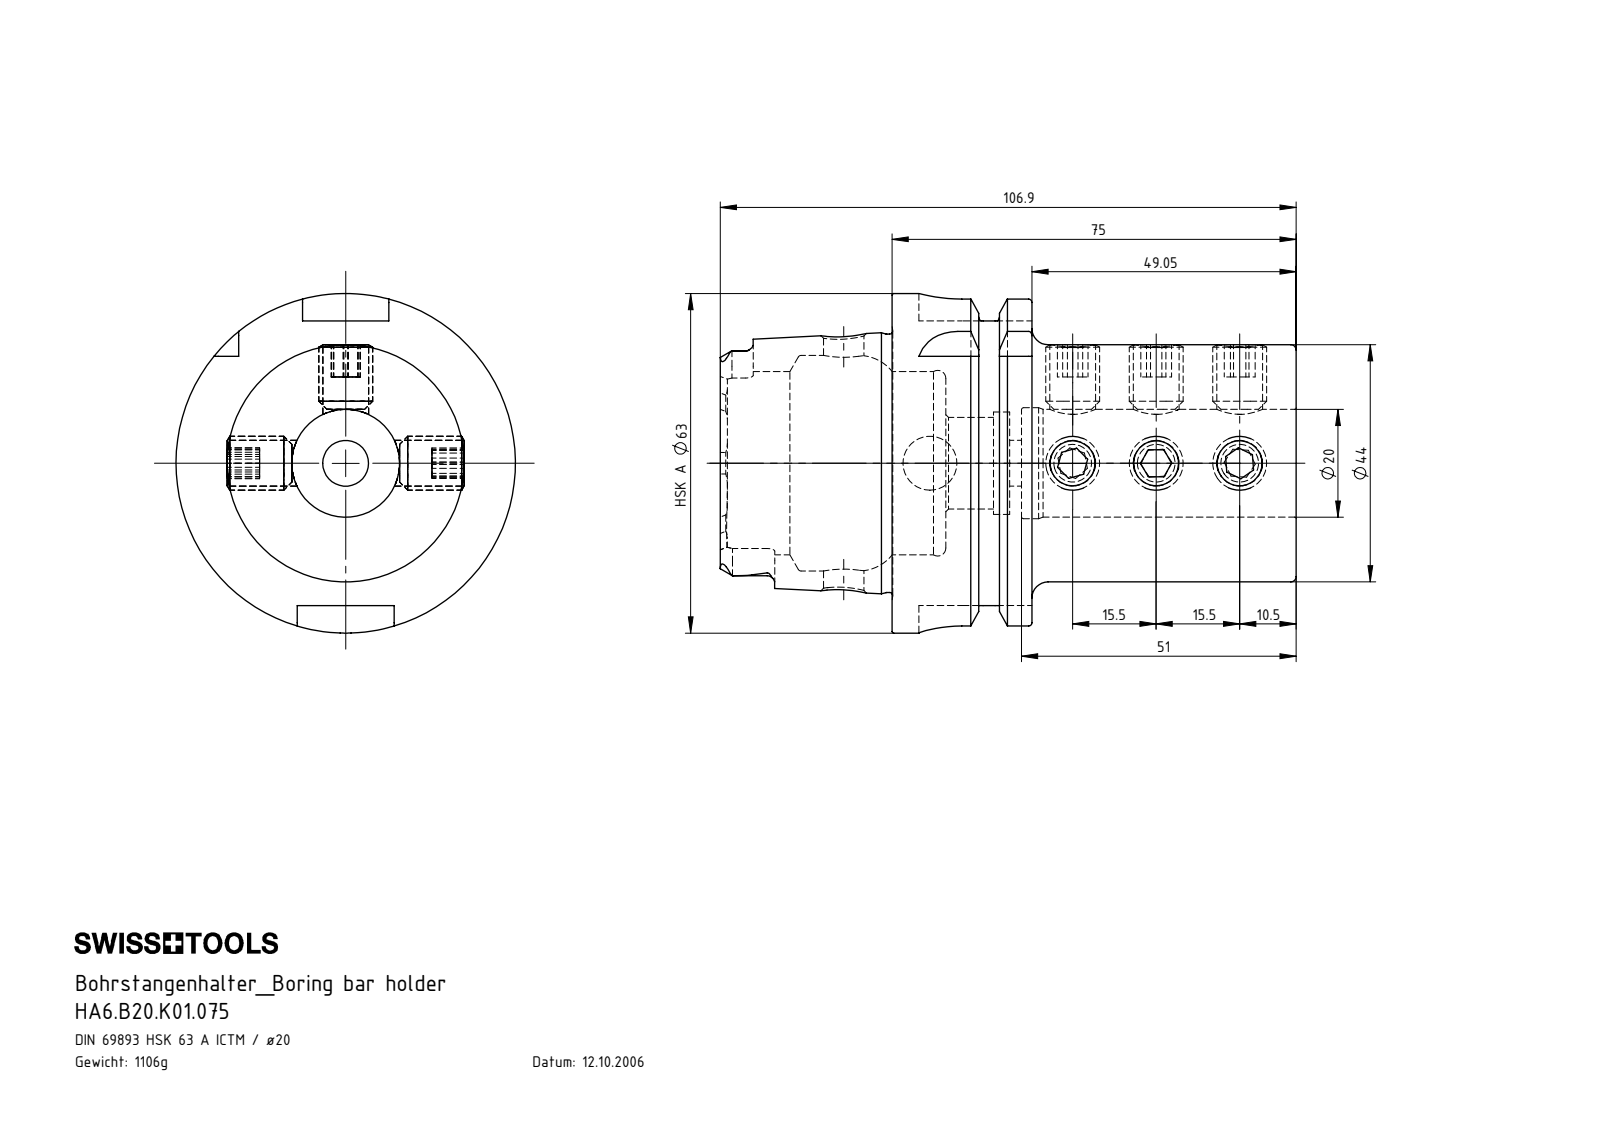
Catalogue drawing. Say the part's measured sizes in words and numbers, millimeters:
The part is named "ISO 4026 - M10 x 12; HA6.B20.K01.075; HA6-B20.K01.075_B_Fertigbearbeitung". Its 3-D file was written by "SolidWorks 2017 (AUTOMOTIVE_DESIGN)". It is 10 solids with 346 faces: 128 planar, 85 cylindrical and 133 other. Overall it measures 106.9 by 63 by 63 millimeters. Its volume is 140 775 cubic millimeters and its surface area 39 112 square millimeters. Round holes: 7 of diameter 8.5, 1 of diameter 7.5, 1 of diameter 10, 1 of diameter 17, 1 of diameter 19, 1 of diameter 20, 1 of diameter 20.6, 1 of diameter 34, 1 of diameter 40. Round bosses or shafts: 6 of diameter 10, 1 of diameter 63, 1 of diameter 54.95, 1 of diameter 47.94, 1 of diameter 44. Partial cylindrical surfaces (rounded edges, fillets, slot ends): 6 of radius 1.4, 4 of radius 2.88, 4 of radius 8. The main face-to-face distances are 75, 25.95, 49.05, 16, 9.95, 65.05, 41.85, 5, 31.9, 57.85. The hole center spacings are 15.5, 31, 26.5, 42, 42.5, 57.5, 58, 73.5.
